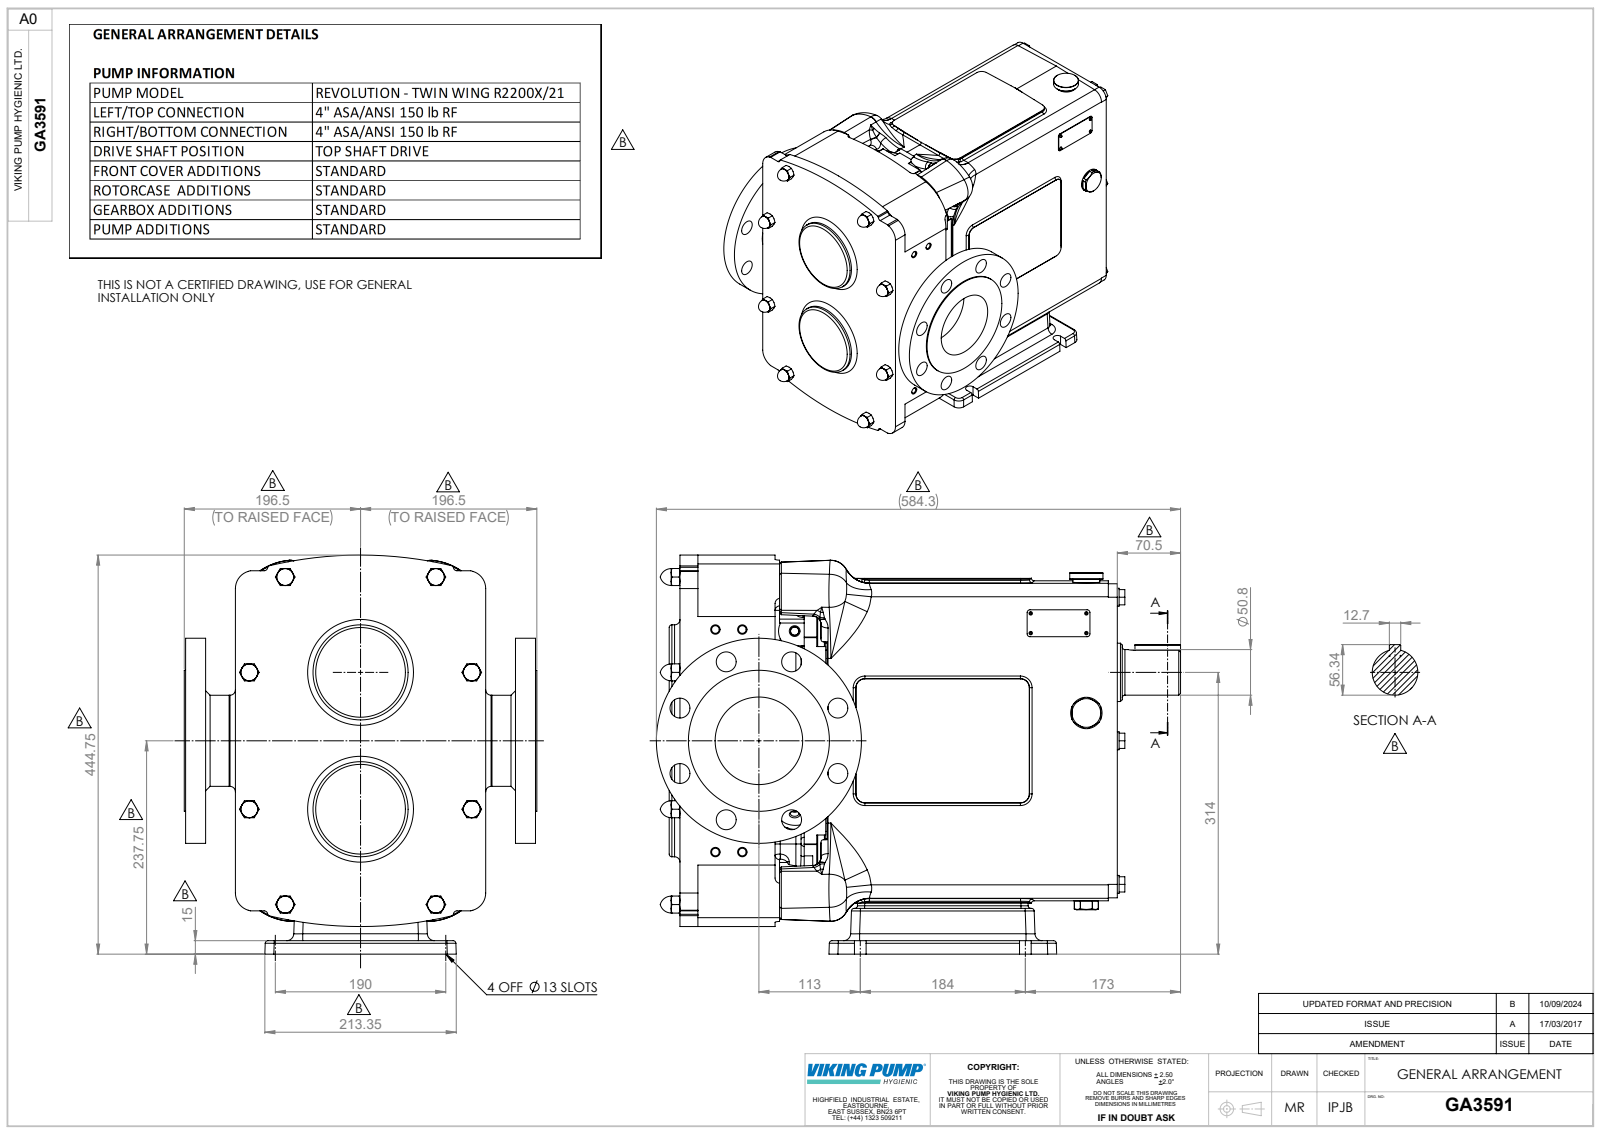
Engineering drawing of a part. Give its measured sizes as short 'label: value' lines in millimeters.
name: Copy of Z94-5301-66 - 4 INCH ASA 150^GA3591; Copy of R2200 CPP H TSD^GA3591; GA3591
written by: SolidWorks 2023 (AUTOMOTIVE_DESIGN)
unit: mm
bodies: 4 solids, 1657 faces (499 planar, 441 cylindrical, 717 other)
size: 584.3 × 444.75 × 393
volume: 40 500 000 mm³; area: 1 428 000 mm²
holes: 8× ⌀22.2, 4× ⌀8.5, 2× ⌀149, 1× ⌀35, 1× ⌀97.6
bosses: 10× ⌀14, 10× ⌀8, 6× ⌀20, 4× ⌀18, 2× ⌀187, 2× ⌀140, 2× ⌀106, 2× ⌀31.5
rounds: 48× R6, 44× R3, 28× R10, 24× R0.2, 16× R1, 16× R5, 10× R8, 8× R15
face distances: 190, 487.5, 77.7, 267.7, 74.7, 270.7, 3, 193, 349, 138.5
hole spacings: 72.9, 95.25, 134.7, 176, 190.5, 30, 37.96, 40.23
